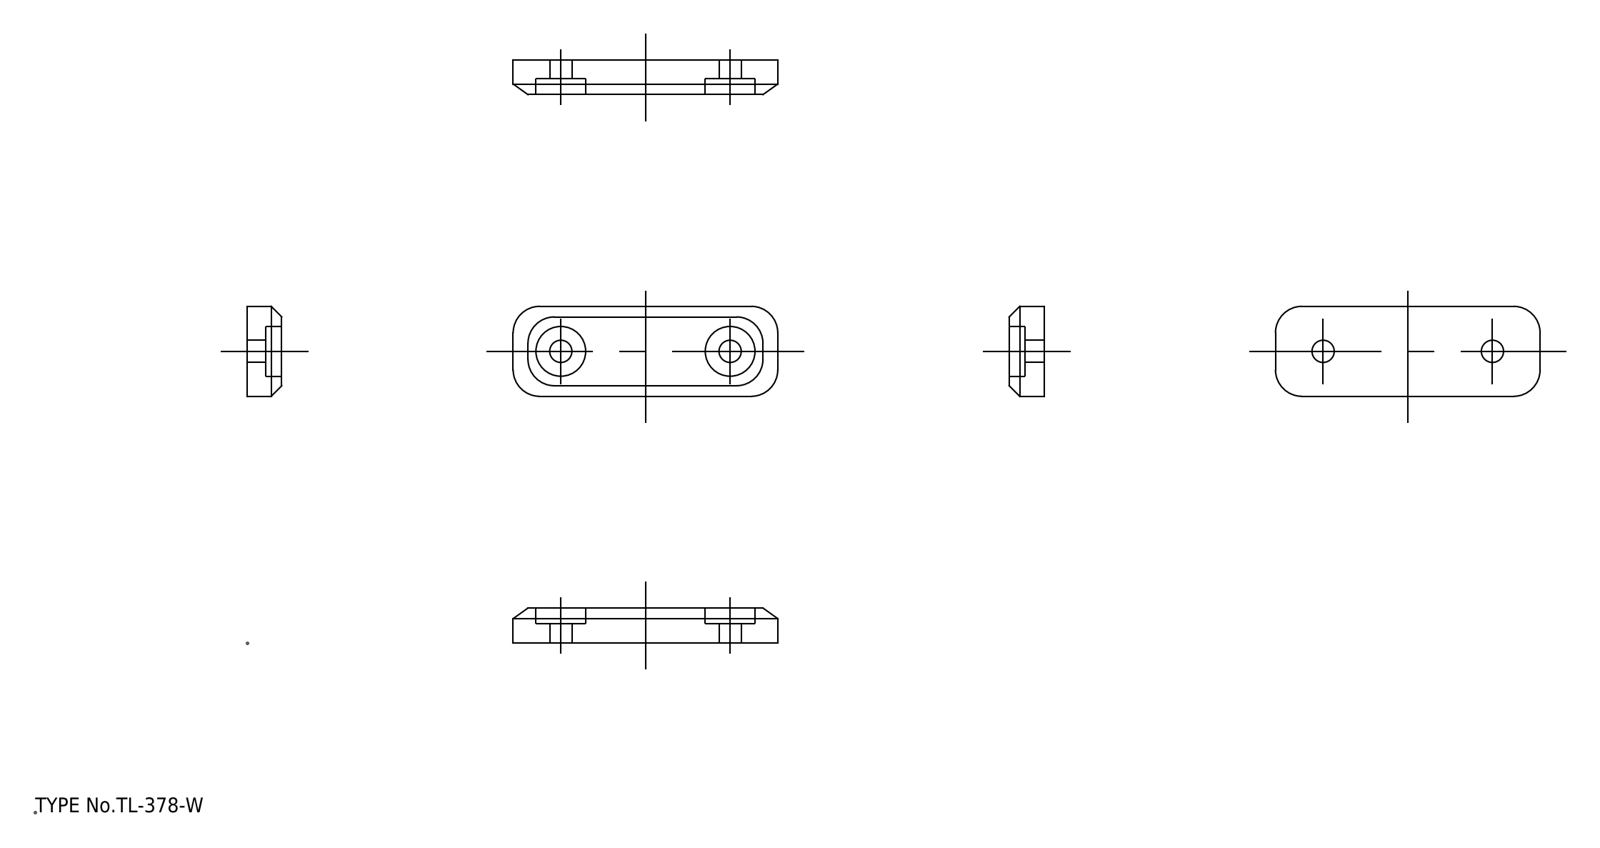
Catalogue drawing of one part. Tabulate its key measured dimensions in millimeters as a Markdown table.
| quantity | value |
| --- | --- |
| part name | magnet |
| STEP written by | spGate 19.8.4 (****-****-****-****) (AUTOMOTIVE_DESIGN) |
| units | millimeters |
| bodies | 1 solid, 28 faces (12 planar, 16 cylindrical, 0 other) |
| overall size | 50 × 17 × 6.6 |
| volume | 4 696 mm³ |
| surface area | 2 547 mm² |
| round holes (diameter × count) | 4.2 × 2, 9.4 × 2 |
| partial cylindrical surfaces (radius × count) | 5 × 8 |
| main face-to-face distances | 6.6, 17, 3, 3.6, 50 |
| hole center spacings | 32 |
